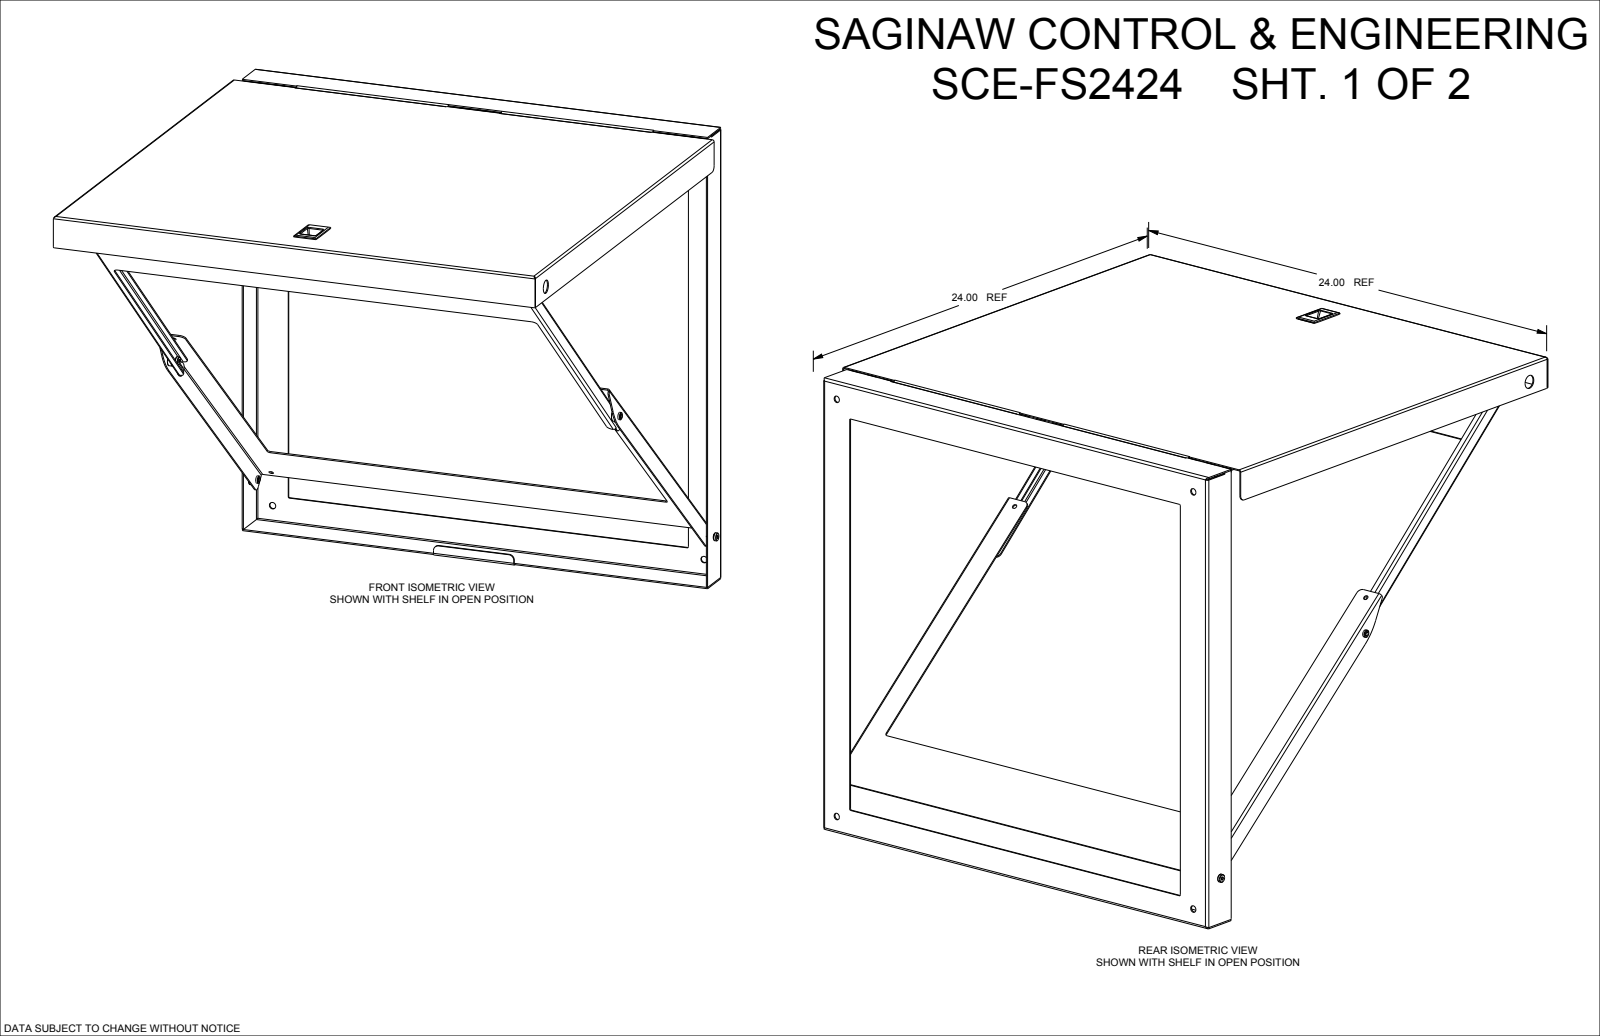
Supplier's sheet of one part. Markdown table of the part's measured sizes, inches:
| quantity | value |
| --- | --- |
| part name | SCE-FS2424_09_SS |
| STEP written by | SolidWorks 2022 (AUTOMOTIVE_DESIGN) |
| units | inches |
| bodies | 66 solids, 2444 faces (1374 planar, 500 cylindrical, 570 other) |
| overall size | 24 × 24 × 21.99 |
| volume | 71.18 in³ |
| surface area | 2 399 in² |
| round holes (diameter × count) | 0.19 × 19, 0.193 × 16, 0.203 × 12, 0.218 × 6, 0.22 × 4, 0.313 × 4, 0.25 × 3, 0.187 × 2, 0.265 × 2, 0.125 × 1, 0.257 × 1, 0.265 × 1 |
| round bosses / shafts (diameter × count) | 0.188 × 19, 0.256 × 16, 0.55 × 3, 0.371 × 3, 0.34 × 3, 0.249 × 3, 0.246 × 3, 0.245 × 1 |
| partial cylindrical surfaces (radius × count) | 0.25 × 19, 0.014 × 16, 0.06 × 15, 0.125 × 13, 0.03 × 7, 0.031 × 7, 0.012 × 5, 0.031 × 5 |
| main face-to-face distances | 0.06, 0.06, 0.406, 23.534, 23.94, 0.012, 21.834, 21.846, 23.128, 24 |
| hole center spacings | 10.219, 10.256, 1.5, 8.719, 11.719, 20.438, 8.763, 11.752 |
